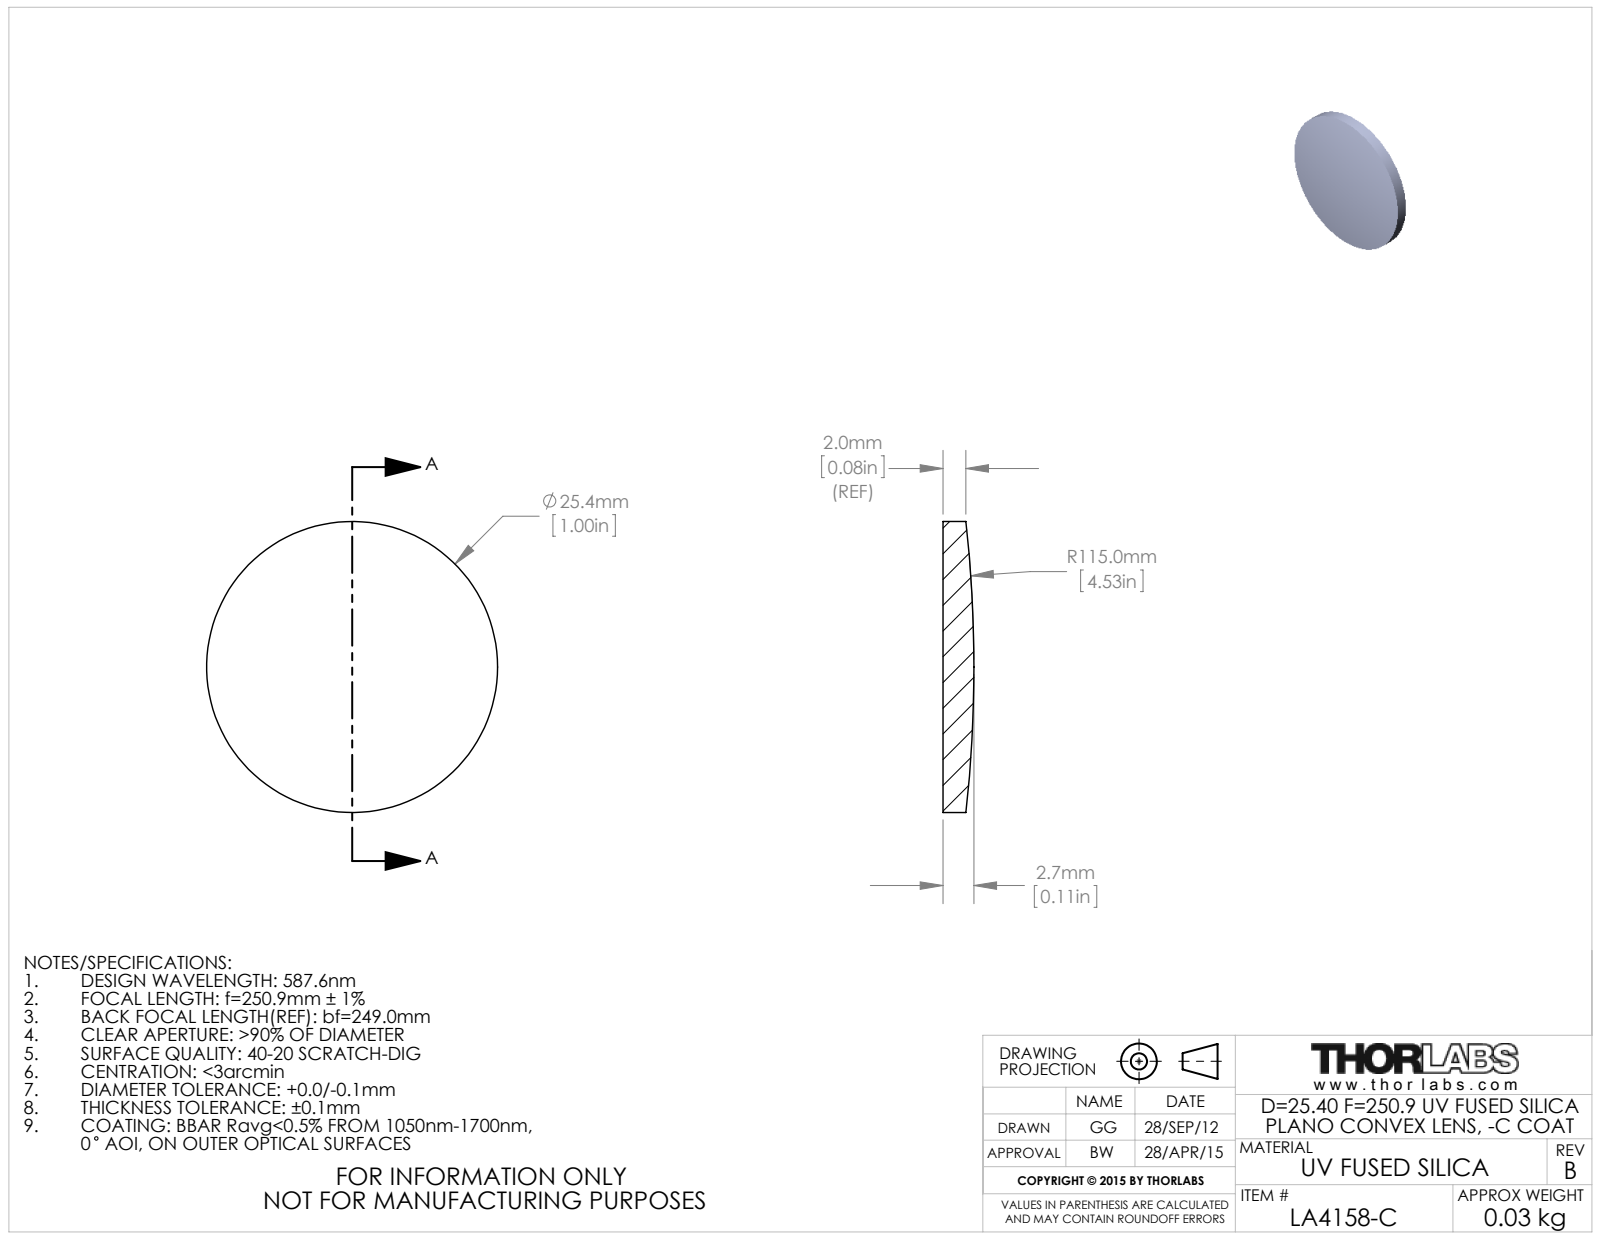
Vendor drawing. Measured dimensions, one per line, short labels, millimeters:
name: 25007-E0W
written by: SolidWorks 2014 (CONFIG_CONTROL_DESIGN)
unit: mm
bodies: 1 solid, 5 faces (1 planar, 2 cylindrical, 2 other)
size: 25.4 × 25.4 × 2.7
volume: 1 191 mm³; area: 1 175 mm²
bosses: 1× ⌀25.4
